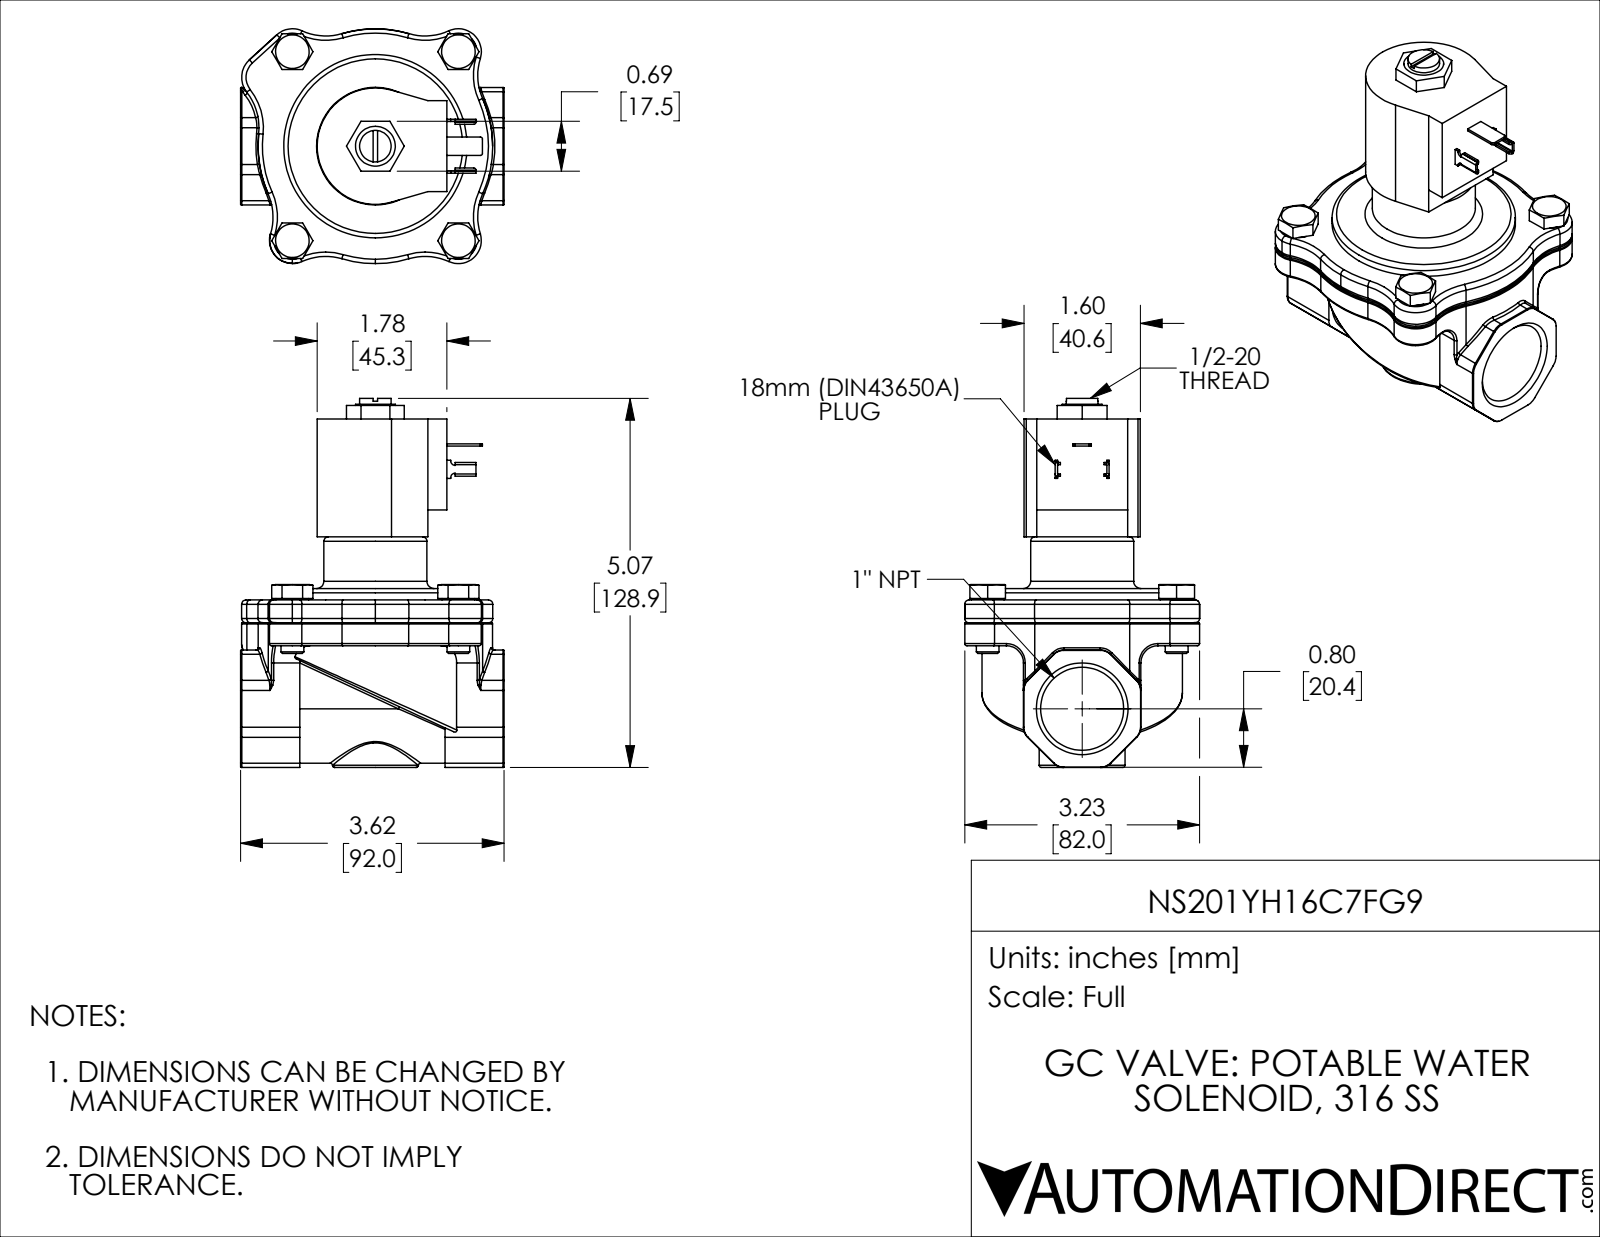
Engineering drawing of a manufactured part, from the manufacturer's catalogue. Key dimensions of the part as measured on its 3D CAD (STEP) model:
Part name (STEP PRODUCT): NS201YH16C7FG9
STEP written by: SolidWorks 2024 (CONFIG_CONTROL_DESIGN)
Units: inches
Bodies: 12 solids, 603 faces (162 planar, 221 cylindrical, 220 other)
Overall size (bounding box): 5.073 × 3.622 × 3.228
Volume: 18.69 in³ · Surface area: 102.4 in²
Round holes (diameter × count): ⌀0.25 ×4, ⌀0.313 ×4, ⌀0.125 ×1, ⌀0.236 ×1, ⌀0.488 ×1, ⌀0.504 ×1, ⌀0.949 ×1, ⌀1.141 ×1, ⌀3 ×1
Round bosses / shafts (diameter × count): ⌀0.45 ×4, ⌀0.313 ×4, ⌀2.65 ×1, ⌀2.52 ×1, ⌀1.417 ×1, ⌀1.181 ×1, ⌀0.547 ×1, ⌀0.434 ×1
Partial cylindrical surfaces — rounded edges, fillets, slot ends (radius × count): R0.031 ×26, R0.787 ×16, R0.03 ×8, R0.197 ×8, R0.315 ×6, R0.06 ×2, R0.236 ×2, R0.327 ×1
Main face-to-face distances: 0.315, 0.03, 0.345, 2.831, 2.801, 2.486, 0.157, 1.211, 1.181, 0.866
Hole centre spacings: 2.598, 1.729, 2.283, 3.458, 1.728, 1.73, 2.274, 2.282
